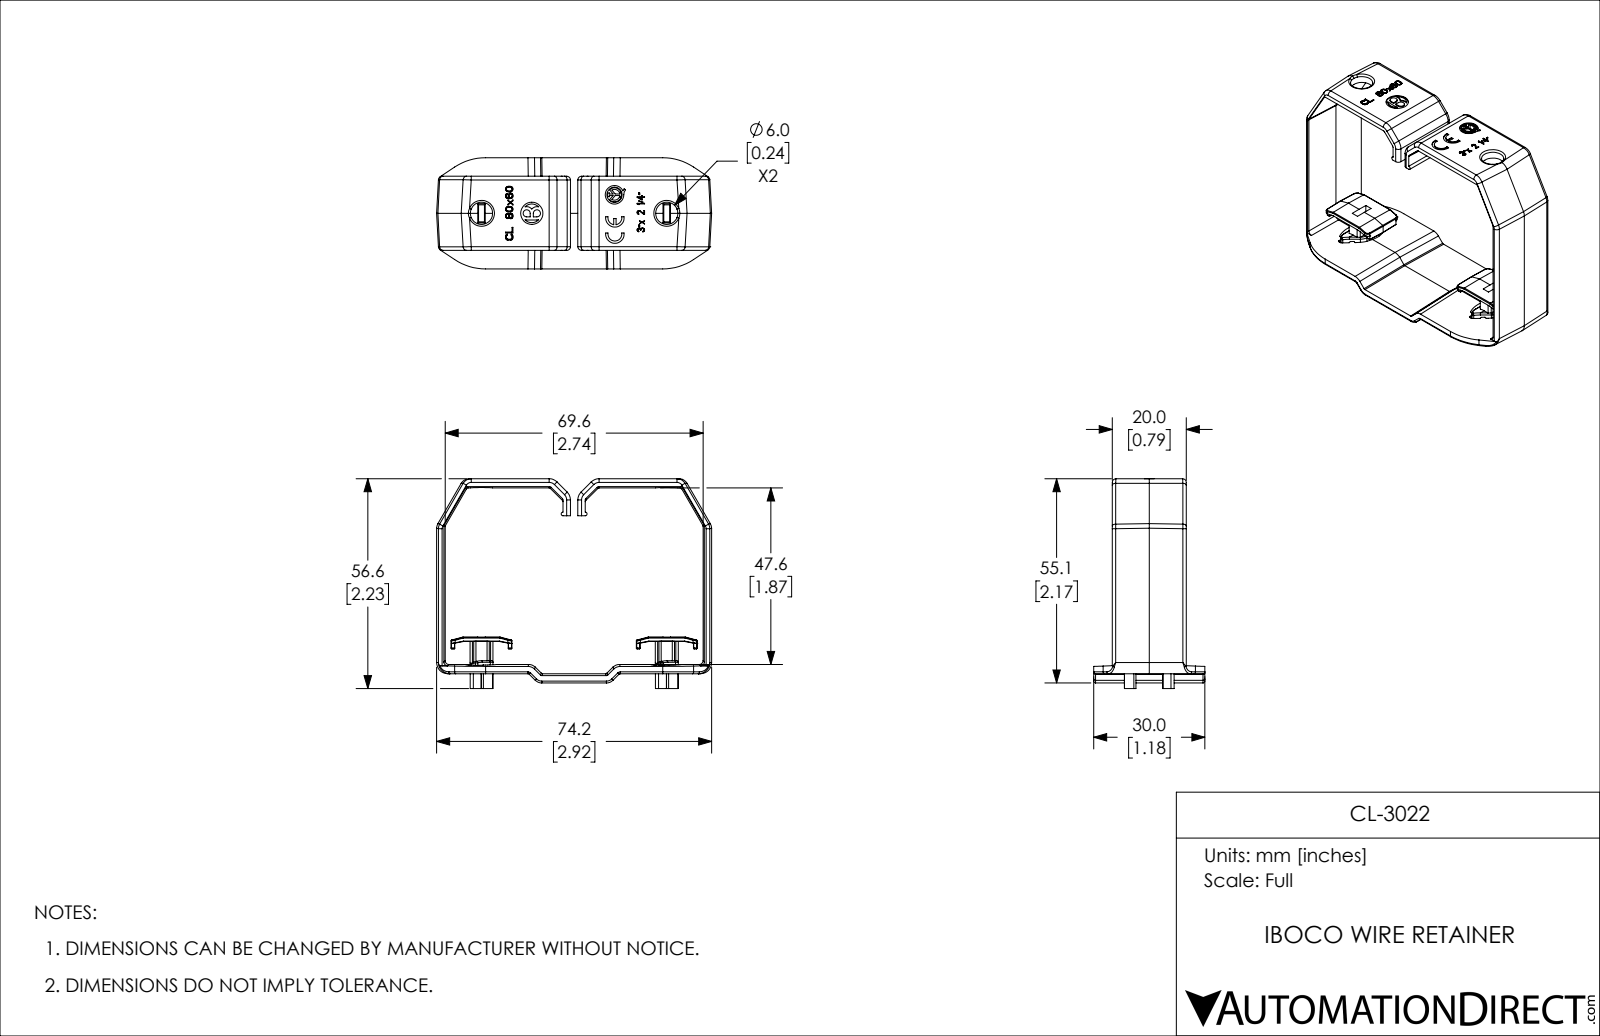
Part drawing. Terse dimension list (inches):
name: CL-3022
written by: SolidWorks 2019 (CONFIG_CONTROL_DESIGN)
unit: in
bodies: 1 solid, 1025 faces (703 planar, 255 cylindrical, 67 other)
size: 2.921 × 2.228 × 1.181
volume: 0.723 in³; area: 20.97 in²
holes: 3× ⌀0.236, 1× ⌀0.197
bosses: 1× ⌀0.161
rounds: 48× R0.02, 36× R0.008, 34× R0.039, 20× R0.098, 12× R0.012, 12× R0.016, 8× R0.118, 4× R0.026
face distances: 0.098, 1.872, 2.738, 2.918, 2.071, 1.97, 2.169, 0.079, 0.157, 0.047
hole spacings: 0.535, 0.589, 0.9, 1.427, 1.434, 1.969
